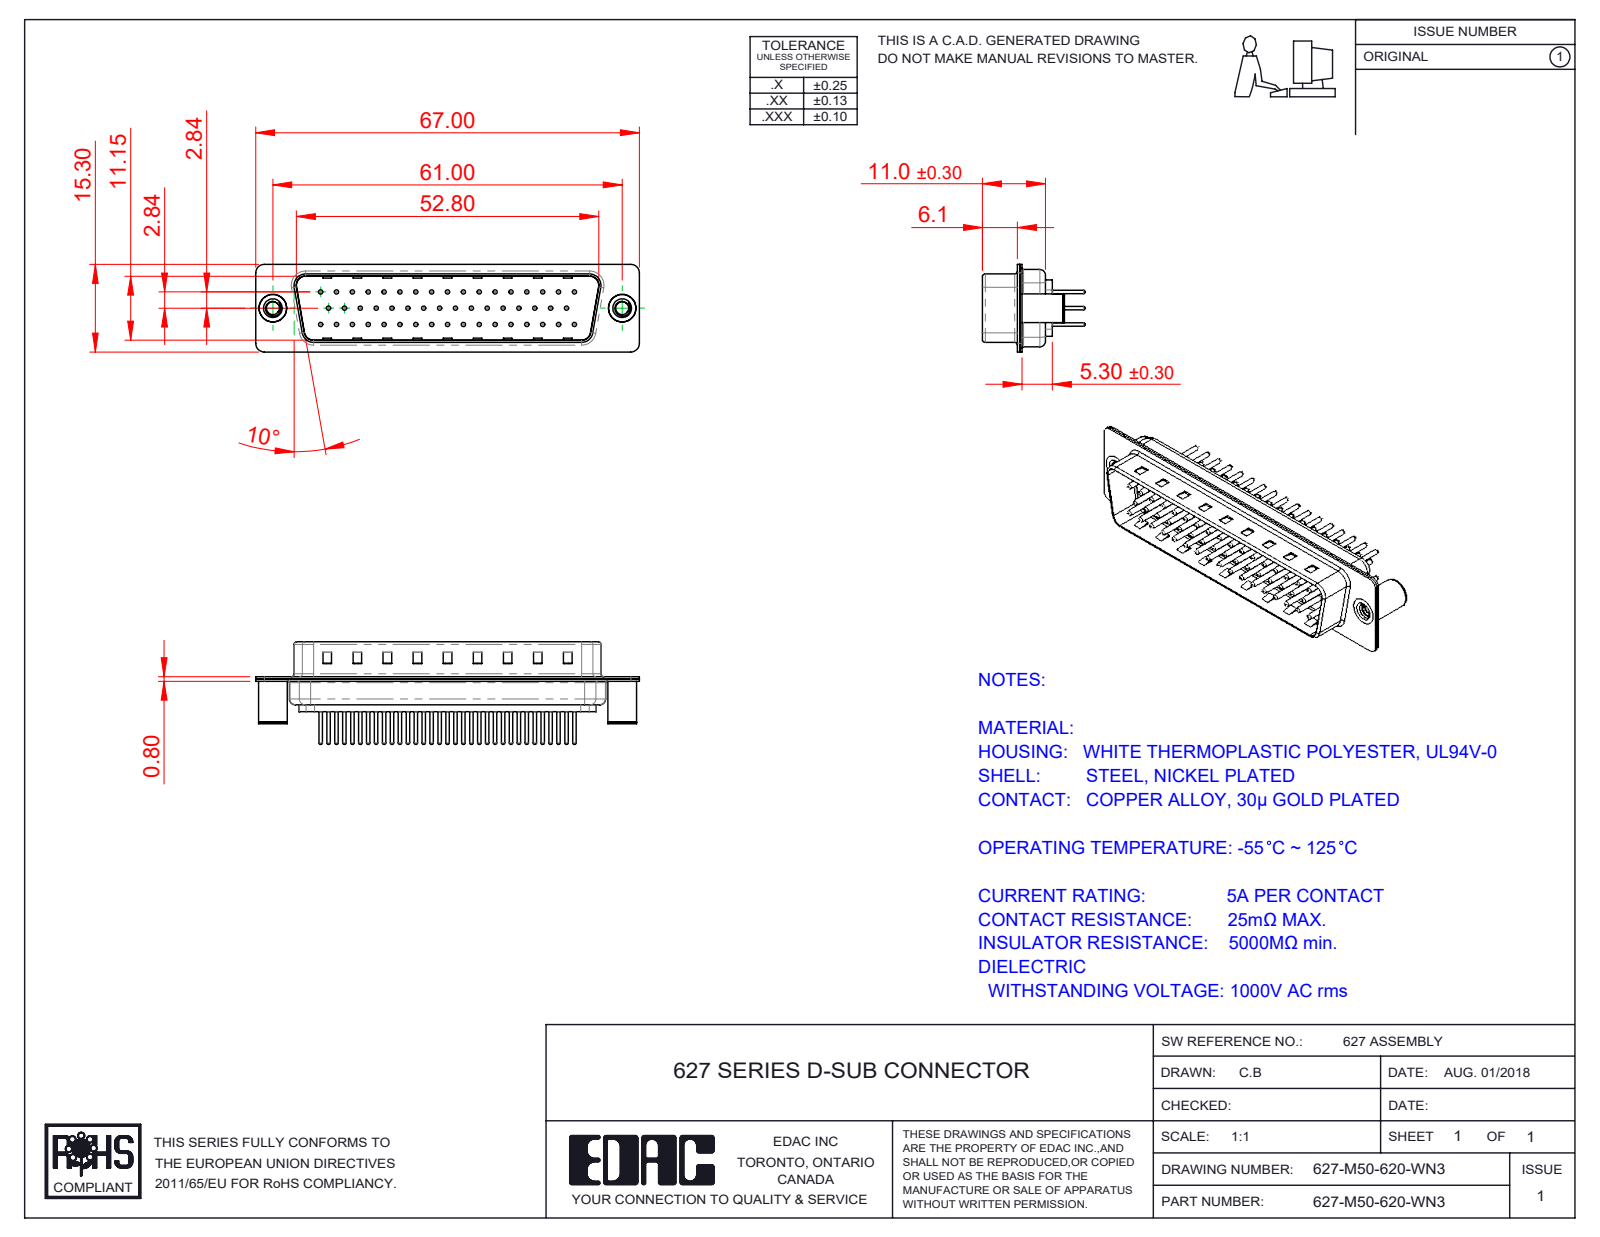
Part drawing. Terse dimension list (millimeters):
name: 627M Shell Rear_50 Contacts; 627M Contact Row 3_20; 627M Contact Row 1_20; 627M Shell Front_50 Contacts (+4 more)
written by: SolidWorks 2020 (CONFIG_CONTROL_DESIGN)
unit: mm
bodies: 55 solids, 2296 faces (553 planar, 865 cylindrical, 878 other)
size: 67 × 17.9 × 15.3
volume: 4 648 mm³; area: 10 957 mm²
holes: 50× ⌀0.75, 50× ⌀1.6, 50× ⌀2, 2× ⌀2.26, 2× ⌀3.26, 2× ⌀4, 2× ⌀4.8
bosses: 50× ⌀1.5, 50× ⌀0.6, 2× ⌀5, 2× ⌀4.9
rounds: 16× R1.5, 12× R2, 8× R0.5, 8× R1.6, 4× R0.25, 4× R0.6, 4× R0.65, 4× R0.9
face distances: 0.4, 11.55, 5.7, 6.1, 0.78, 0.77, 12.33, 5.3, 12.32, 13.1
hole spacings: 3.16, 2.77, 5.54, 8.31, 11.08, 13.85, 16.62, 5.03
